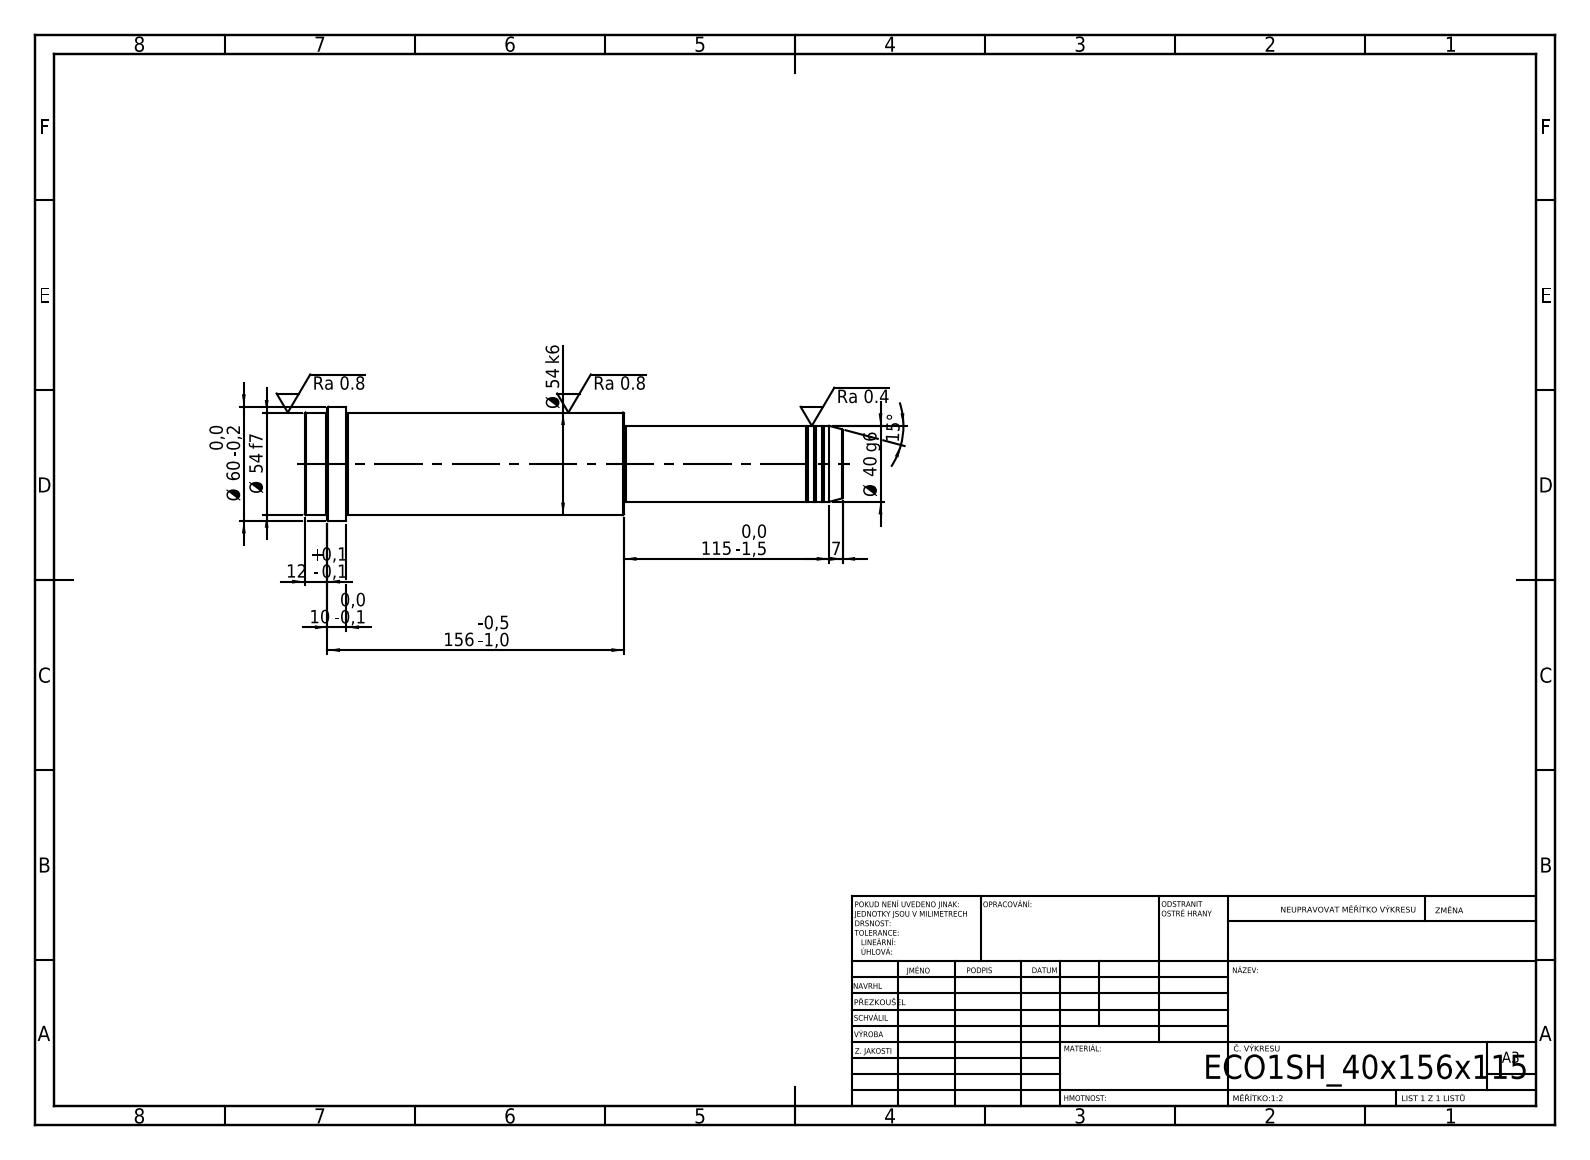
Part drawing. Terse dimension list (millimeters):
written by: SolidWorks 2019 (CONFIG_CONTROL_DESIGN)
unit: mm
bodies: 1 solid, 52 faces (6 planar, 16 cylindrical, 30 other)
size: 283 × 60 × 60
volume: 533 434 mm³; area: 48 905 mm²
bosses: 1× ⌀60, 1× ⌀54, 1× ⌀40, 1× ⌀39
face distances: 168, 115, 283, 261, 146, 22, 271, 156, 10, 12
